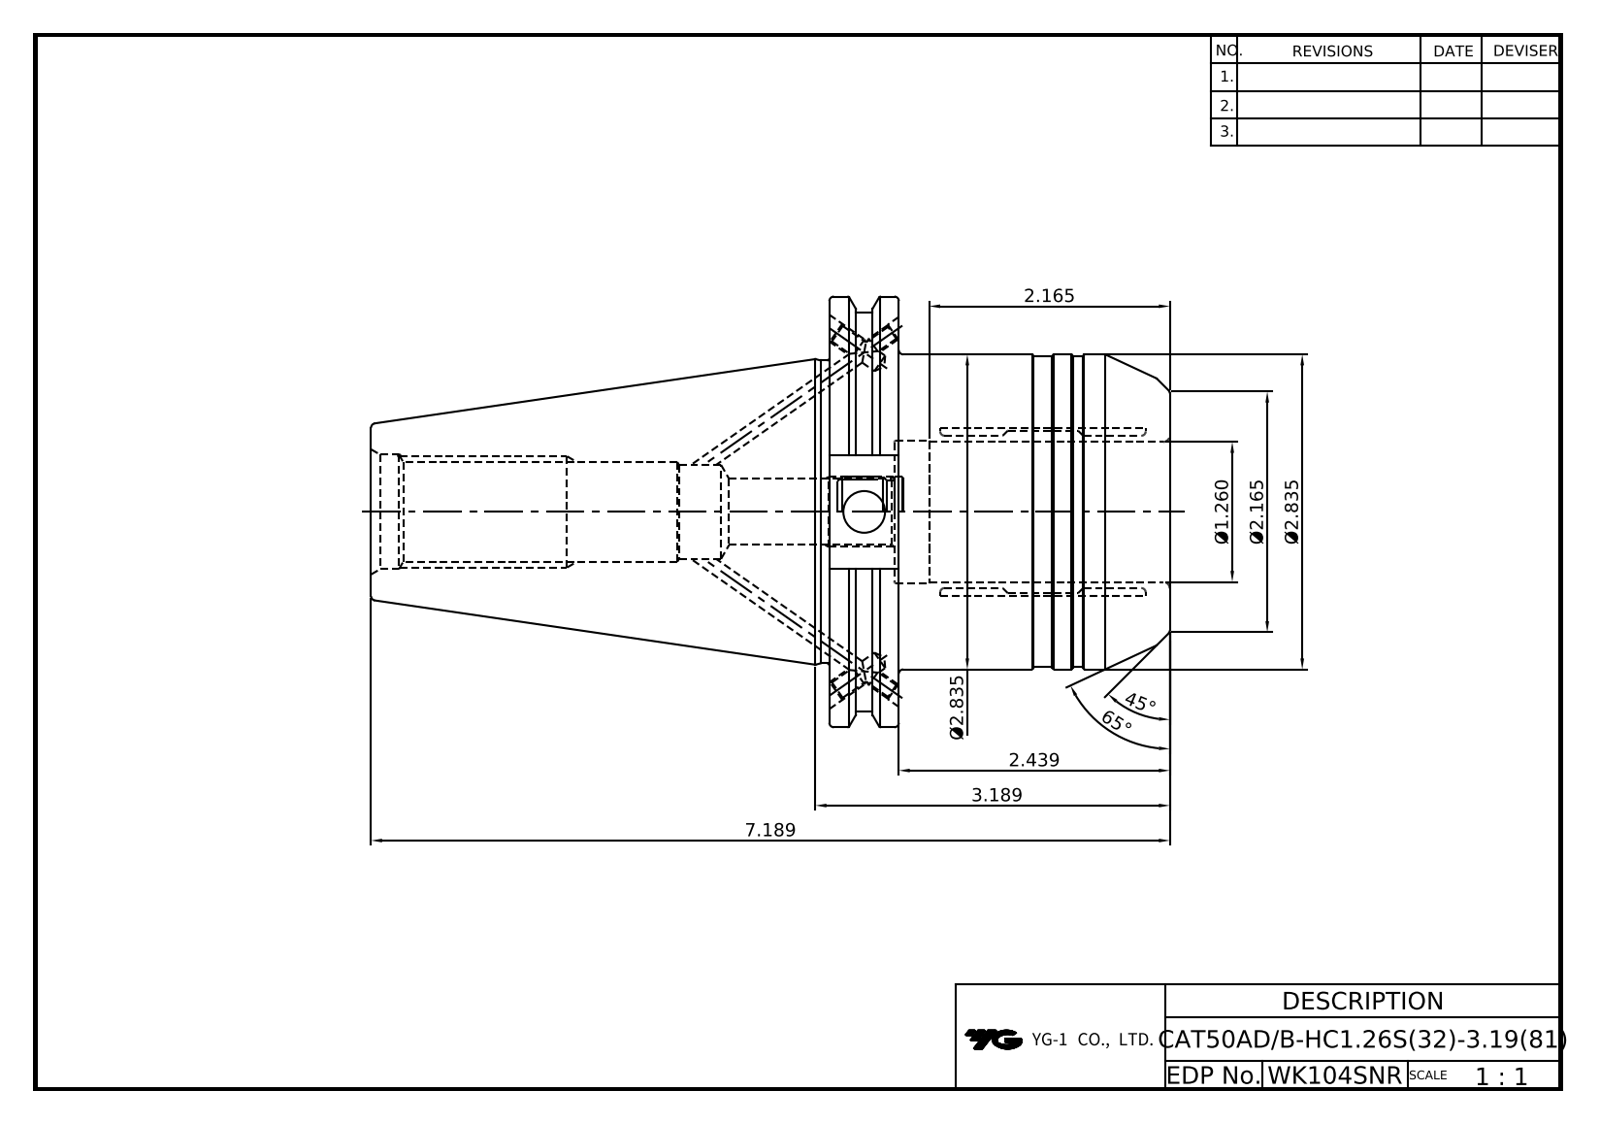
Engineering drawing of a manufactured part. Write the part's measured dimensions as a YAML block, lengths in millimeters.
part_name: "LO-CAT50ADB-HC32S-81"
step_written_by: "Autodesk Inventor 2020 (AUTOMOTIVE_DESIGN)"
units: millimeters
bodies: {solids: 1, faces: 103, planar: 32, cylindrical: 32, other: 39}
overall_size: [182.6, 98.42, 94.69]
volume: 514670
surface_area: 63598
round_holes:
  - {diameter: 4.13, count: 4}
  - {diameter: 5, count: 4}
  - {diameter: 9.53, count: 1}
  - {diameter: 14.92, count: 1}
  - {diameter: 21.5, count: 1}
  - {diameter: 21.97, count: 1}
  - {diameter: 26.2, count: 1}
  - {diameter: 32, count: 1}
  - {diameter: 32.6, count: 1}
round_bosses_or_shafts:
  - {diameter: 98.42, count: 1}
  - {diameter: 91.29, count: 1}
  - {diameter: 72, count: 1}
  - {diameter: 71, count: 1}
  - {diameter: 69.25, count: 1}
partial_cylinders:
  - {radius: 12.45, count: 1}
face_to_face_distances: [15.88, 77.83, 61.95, 14.83, 1.05, 63, 104.77, 119.6, 120.65, 182.6]
hole_center_spacings: [59.7]
